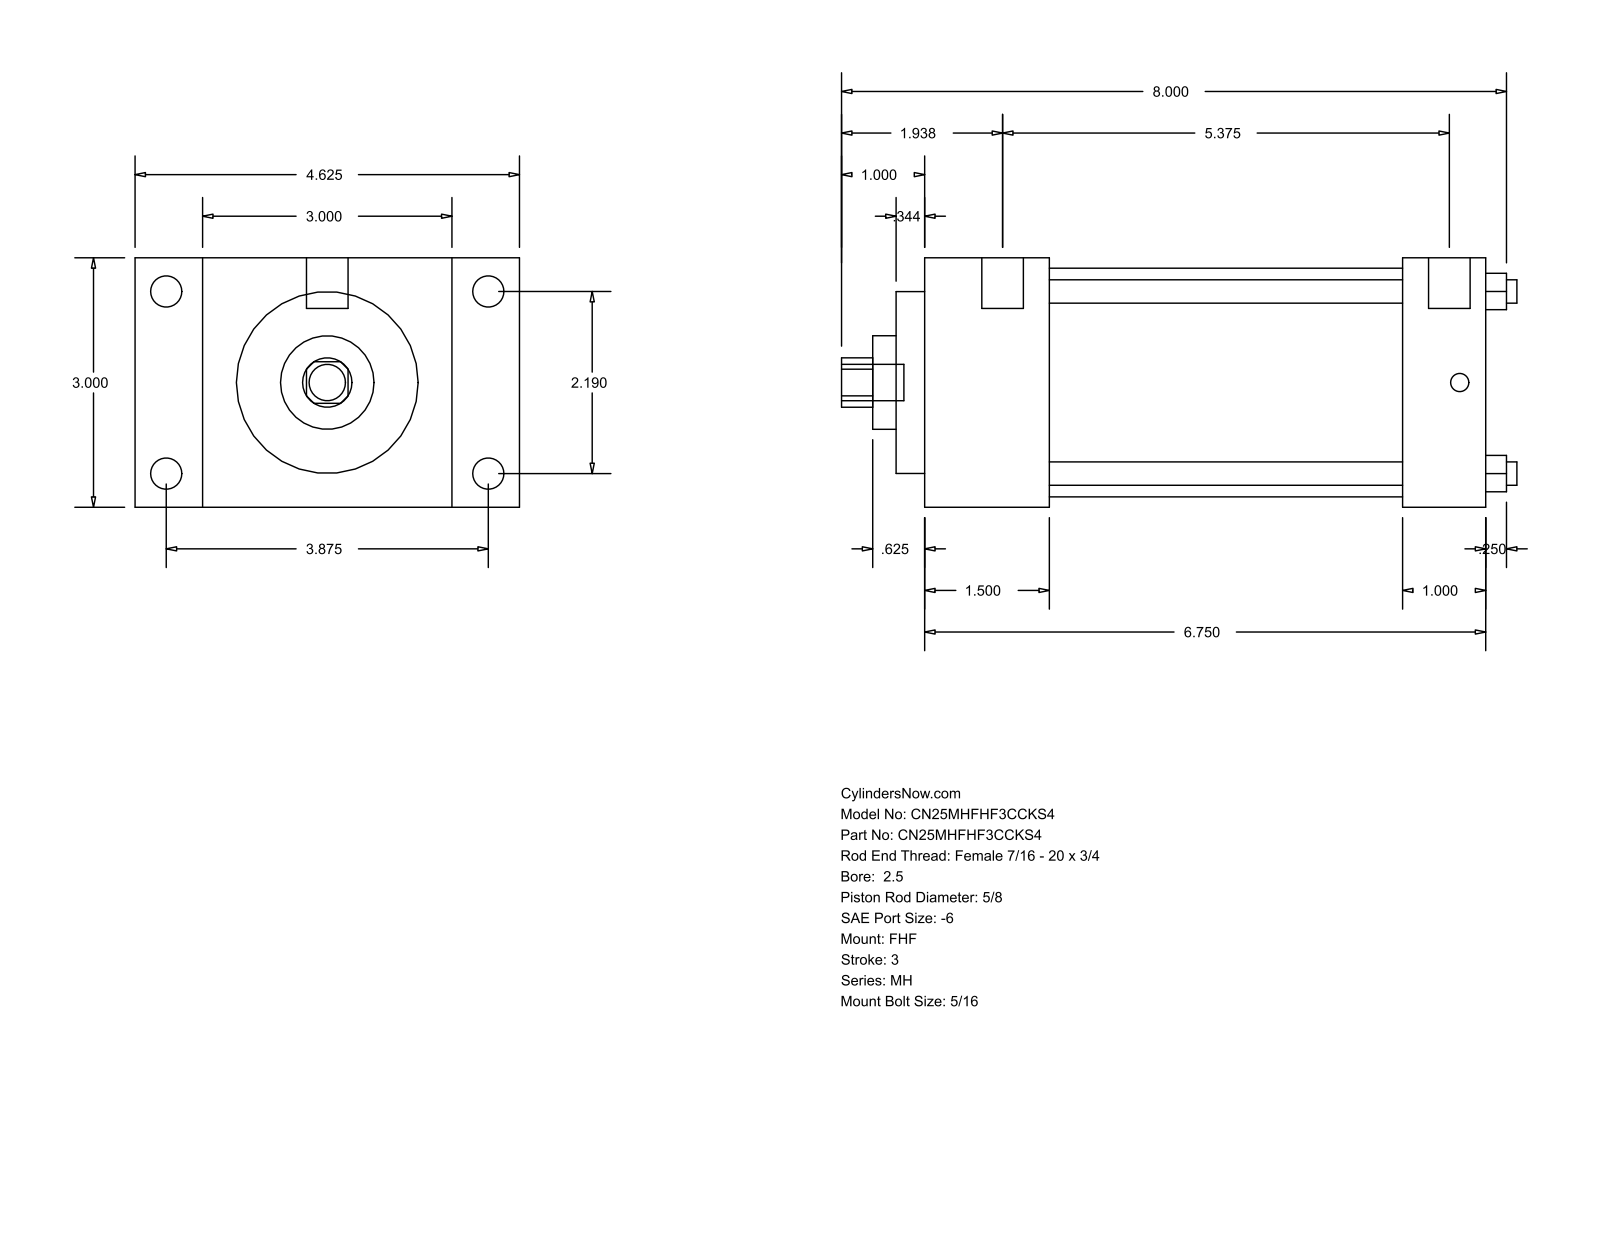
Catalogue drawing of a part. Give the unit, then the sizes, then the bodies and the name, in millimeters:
Units: millimetres
Overall size (bounding box): 206.38 × 117.47 × 76.2
Round holes (diameter × count): ⌀7.14 ×4, ⌀15.88 ×1, ⌀28.57 ×1, ⌀55.55 ×1, ⌀69.85 ×1
Round bosses / shafts (diameter × count): ⌀9.53 ×4, ⌀5.56 ×4, ⌀12.7 ×2, ⌀11.11 ×1
Partial cylindrical surfaces — rounded edges, fillets, slot ends (radius × count): R7.54 ×1
Main face-to-face distances: 76.2, 171.45, 38.1, 133.35, 20.64, 96.84, 117.48, 25.4, 146.05, 107.95
Hole centre spacings: 39.33, 55.62, 78.66
Bodies: 0 solids, 90 faces (61 planar, 29 cylindrical, 0 other)
Part name (STEP PRODUCT): MH_FHF__0250_0.625
STEP written by: GSSL Pune (CONFIG_CONTROL_DESIGN)
